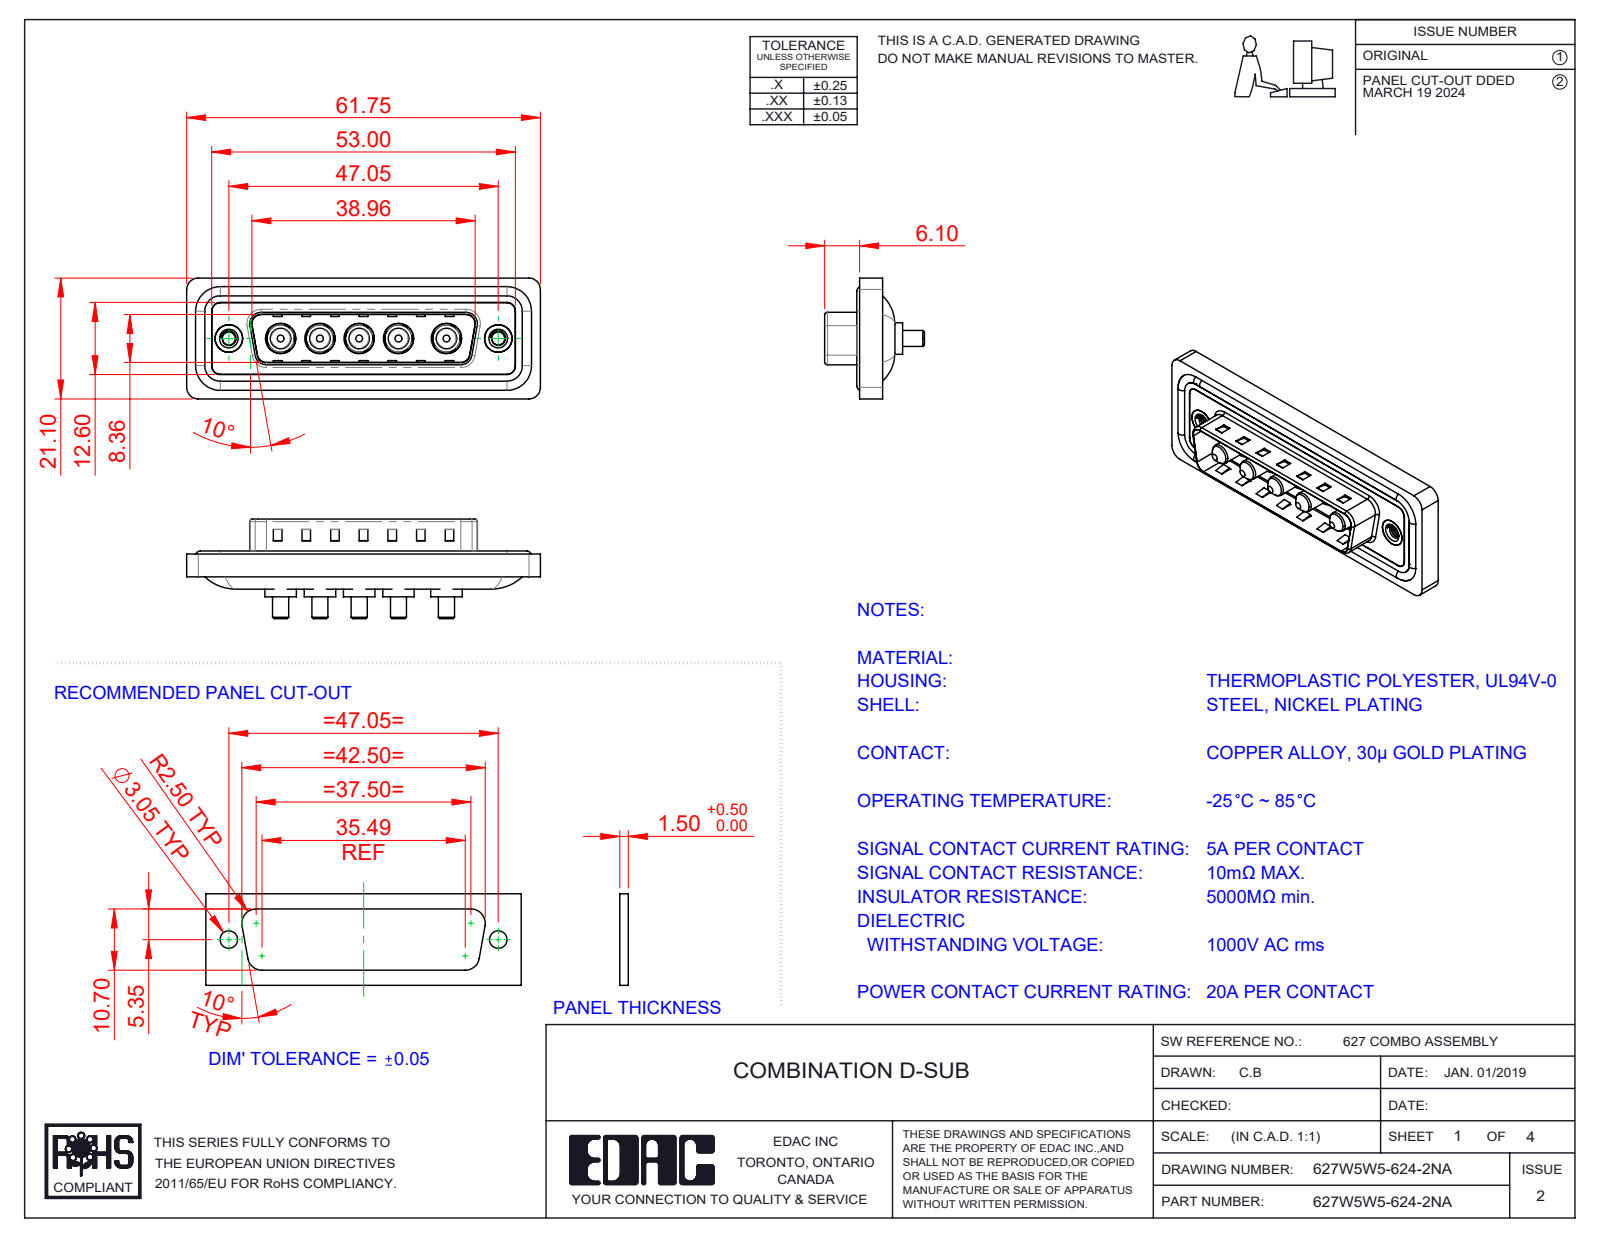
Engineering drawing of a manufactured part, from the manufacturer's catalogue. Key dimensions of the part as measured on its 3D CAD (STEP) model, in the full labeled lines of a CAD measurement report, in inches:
Part name (STEP PRODUCT): 627Combo Shell Front_25 Contacts; 627W5W5-624-2NA; 627Combo Waterproof Housing_25 Contacts; 627Combo Threaded Rivet_A (+3 more)
STEP written by: SolidWorks 2023 (CONFIG_CONTROL_DESIGN)
Units: inches
Bodies: 17 solids, 676 faces (259 planar, 285 cylindrical, 132 other)
Overall size (bounding box): 2.431 × 0.831 × 0.685
Volume: 0.456 in³ · Surface area: 18.28 in²
Round holes (diameter × count): ⌀0.191 ×5, ⌀0.209 ×5, ⌀0.089 ×2, ⌀0.157 ×2, ⌀0.189 ×2, ⌀0.197 ×2
Round bosses / shafts (diameter × count): ⌀0.217 ×5, ⌀0.205 ×5, ⌀0.187 ×5, ⌀0.148 ×5, ⌀0.142 ×5, ⌀0.11 ×5, ⌀0.063 ×4, ⌀0.193 ×2
Partial cylindrical surfaces — rounded edges, fillets, slot ends (radius × count): R0.059 ×22, R0.079 ×18, R0.02 ×8, R0.063 ×8, R0.083 ×5, R0.01 ×4, R0.024 ×4, R0.026 ×4
Main face-to-face distances: 0.016, 0.059, 0.02, 0.043, 0.122, 0.063, 0.114, 0.032, 0.377, 0.222
Hole centre spacings: 0.27, 0.356, 0.541, 1.496, 0.27, 0.33, 0.33, 0.356
